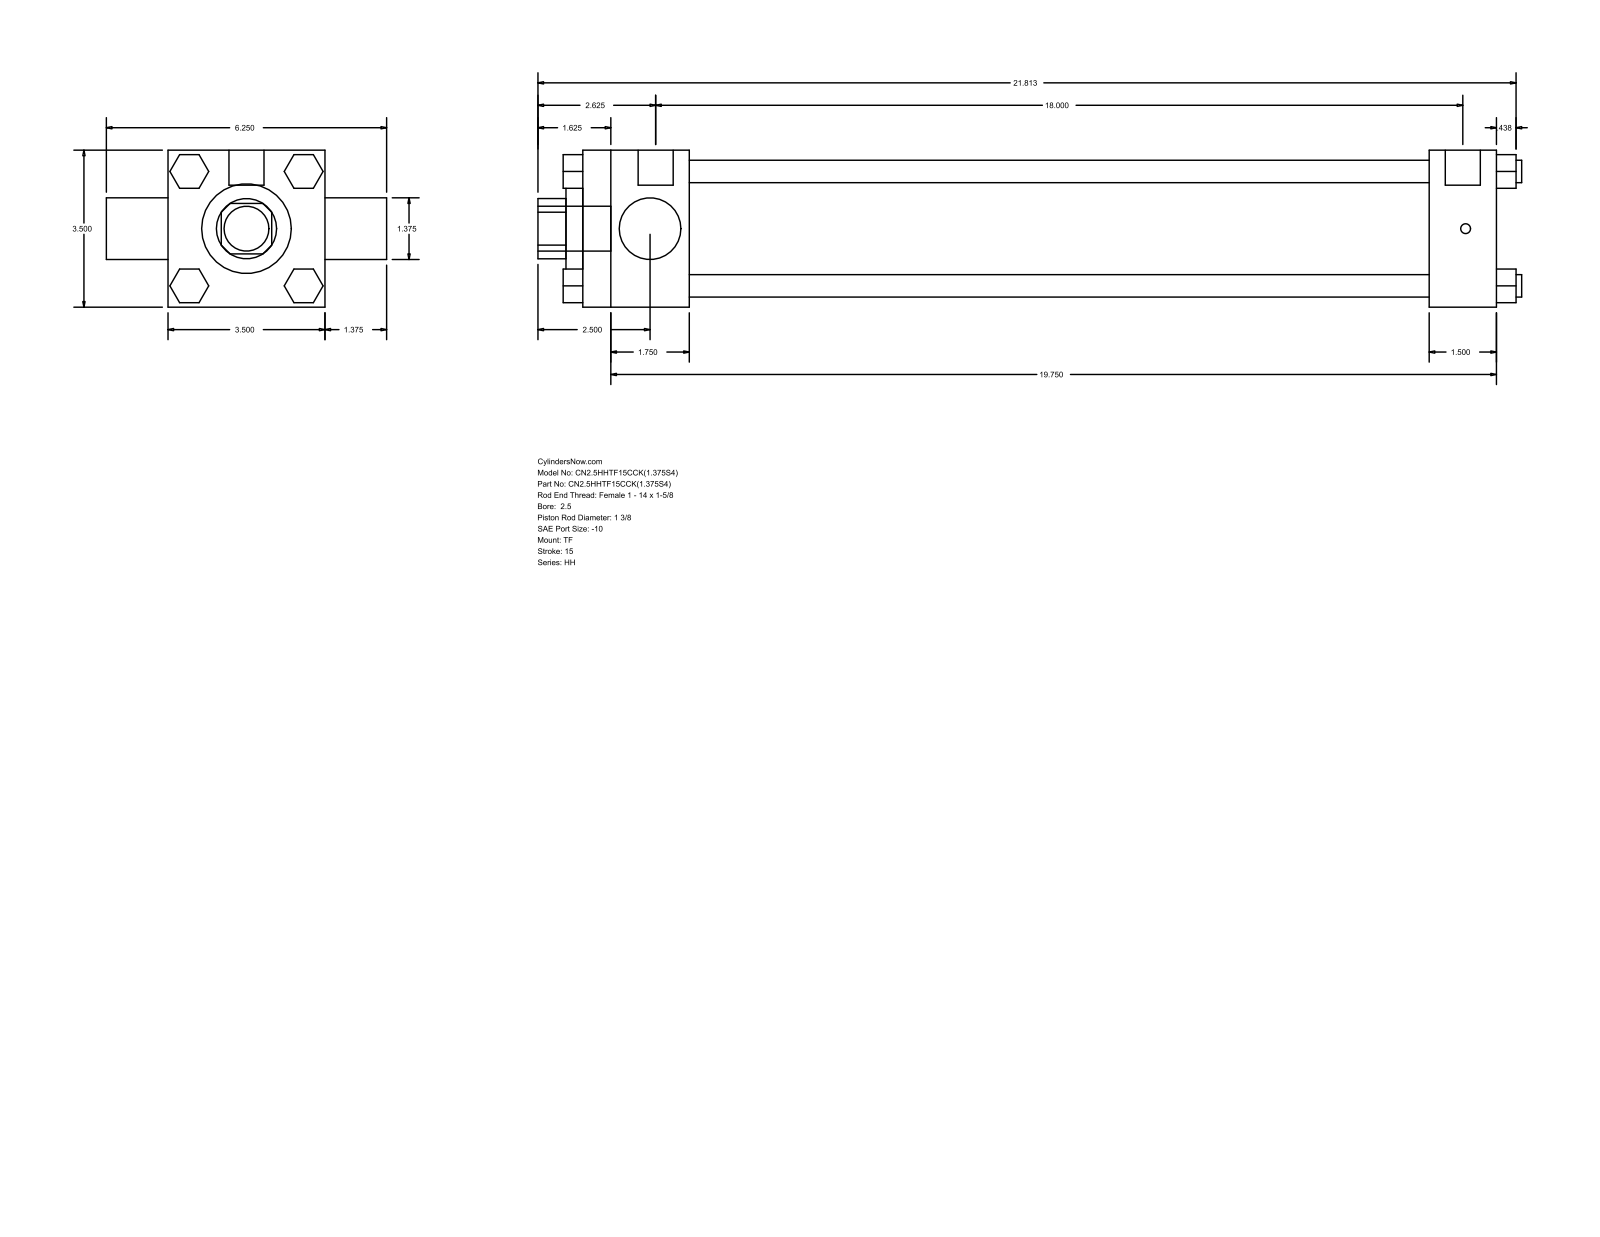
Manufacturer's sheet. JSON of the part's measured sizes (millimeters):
{"part_name": "HH_TF__0250_1.375", "step_written_by": "GSSL Pune (CONFIG_CONTROL_DESIGN)", "units": "millimeters", "bodies": {"solids": 0, "faces": 120, "planar": 92, "cylindrical": 28, "other": 0}, "overall_size": [557.21, 158.75, 88.9], "round_holes": [[34.92, 2], [50.8, 1], [73.03, 1]], "round_bosses_or_shafts": [[12.7, 4], [5.56, 3], [19.84, 2], [25.4, 1]], "partial_cylinders_radius": [[17.06, 1]], "face_to_face_distances": [88.9, 517.52, 60.32, 457.2, 479.42, 419.1, 38.1, 19.05, 32.38, 56.09]}
